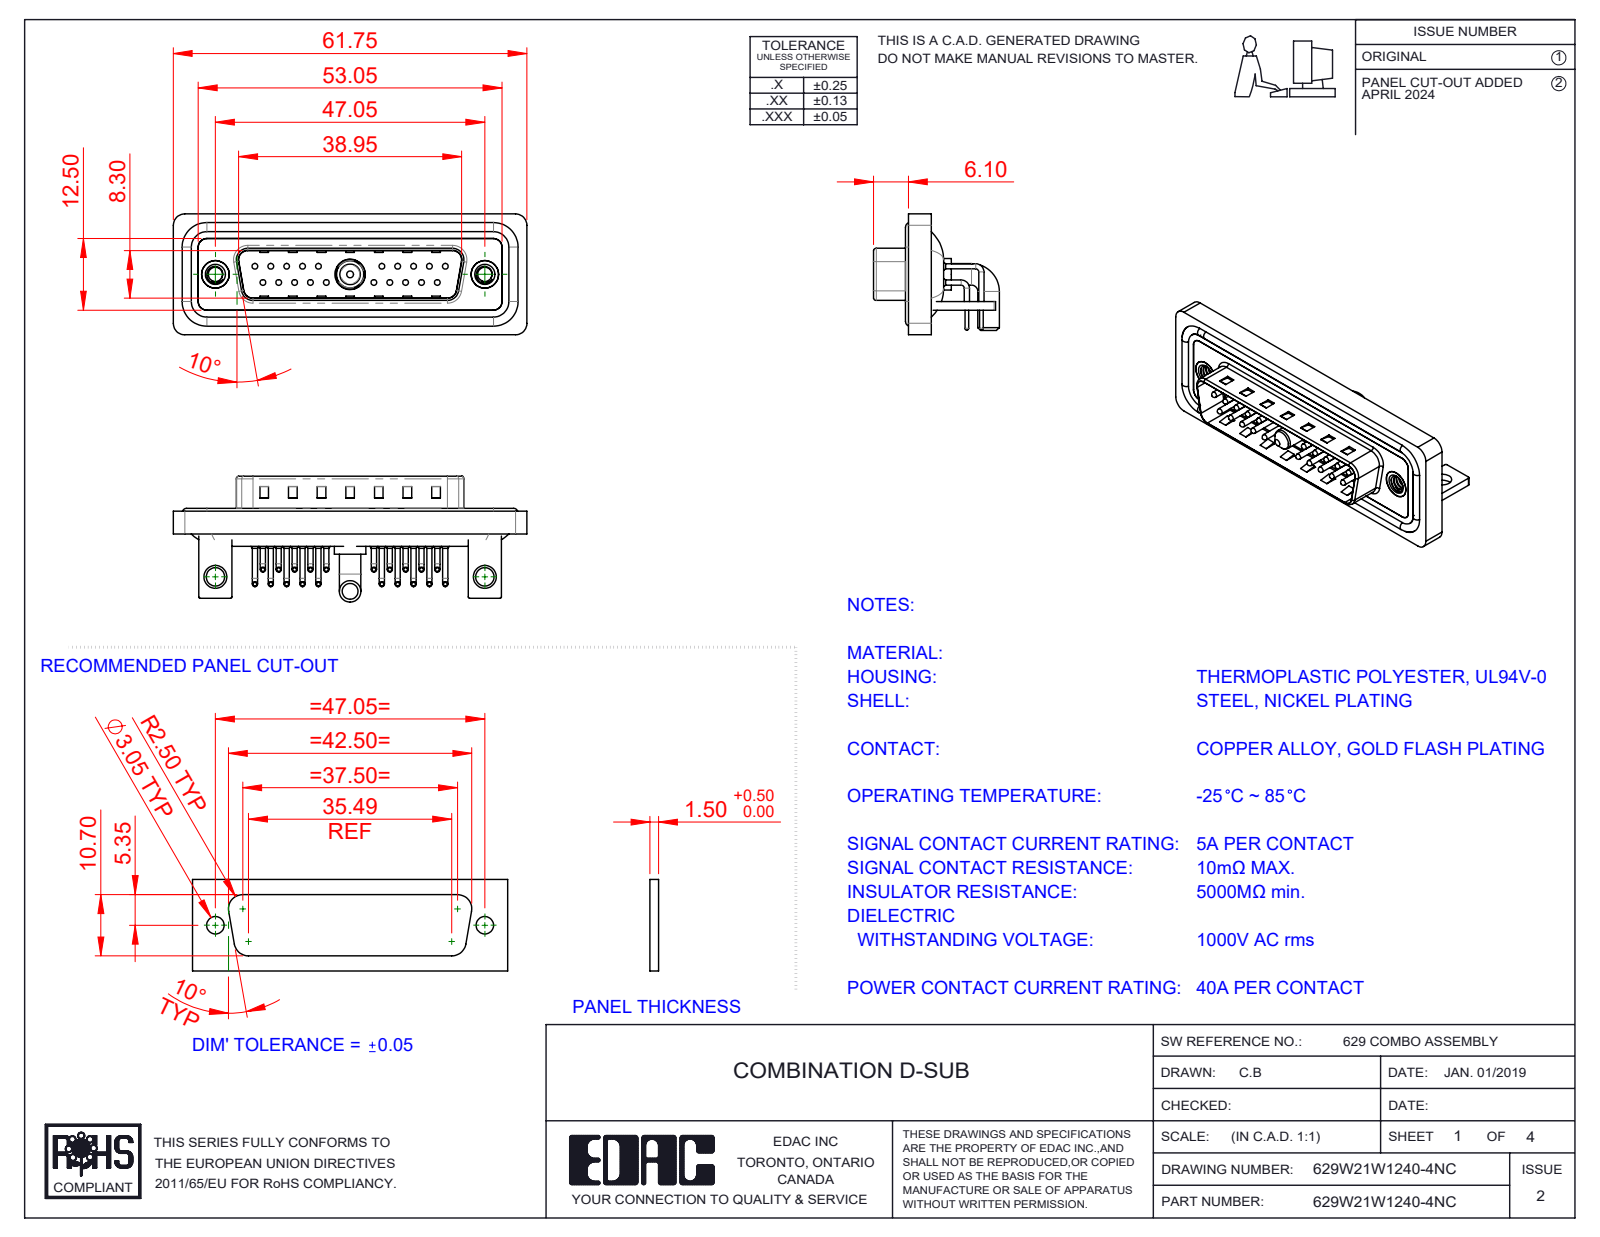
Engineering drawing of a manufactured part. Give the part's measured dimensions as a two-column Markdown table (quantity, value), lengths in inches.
| quantity | value |
| --- | --- |
| part name | 629Combo Waterproof Housing_25 Contacts; 629Combo Contact Row 2; 629Combo Housing_21W1; 629Combo Shell Front_25 Contacts (+6 more) |
| STEP written by | SolidWorks 2023 (CONFIG_CONTROL_DESIGN) |
| units | inches |
| bodies | 31 solids, 2764 faces (1519 planar, 947 cylindrical, 298 other) |
| overall size | 2.431 × 0.865 × 0.831 |
| volume | 0.474 in³ |
| surface area | 20.7 in² |
| round holes (diameter × count) | 0.03 × 20, 0.063 × 20, 0.079 × 20, 0.098 × 2, 0.126 × 2, 0.157 × 2, 0.189 × 2, 0.197 × 2, 0.191 × 1, 0.209 × 1 |
| round bosses / shafts (diameter × count) | 0.035 × 40, 0.059 × 20, 0.039 × 20, 0.026 × 20, 0.063 × 4, 0.193 × 2, 0.148 × 2, 0.217 × 1 |
| partial cylindrical surfaces (radius × count) | 0.04 × 20, 0.079 × 19, 0.059 × 18, 0.01 × 16, 0.02 × 9, 0.063 × 8, 0.024 × 4, 0.026 × 4 |
| main face-to-face distances | 0.016, 0.031, 0.083, 0.114, 0.059, 0.043, 0.161, 0.063, 0.177, 0.146 |
| hole center spacings | 0.124, 0.109, 0.218, 0.327, 0.198, 0.763, 0.826, 0.872 |
